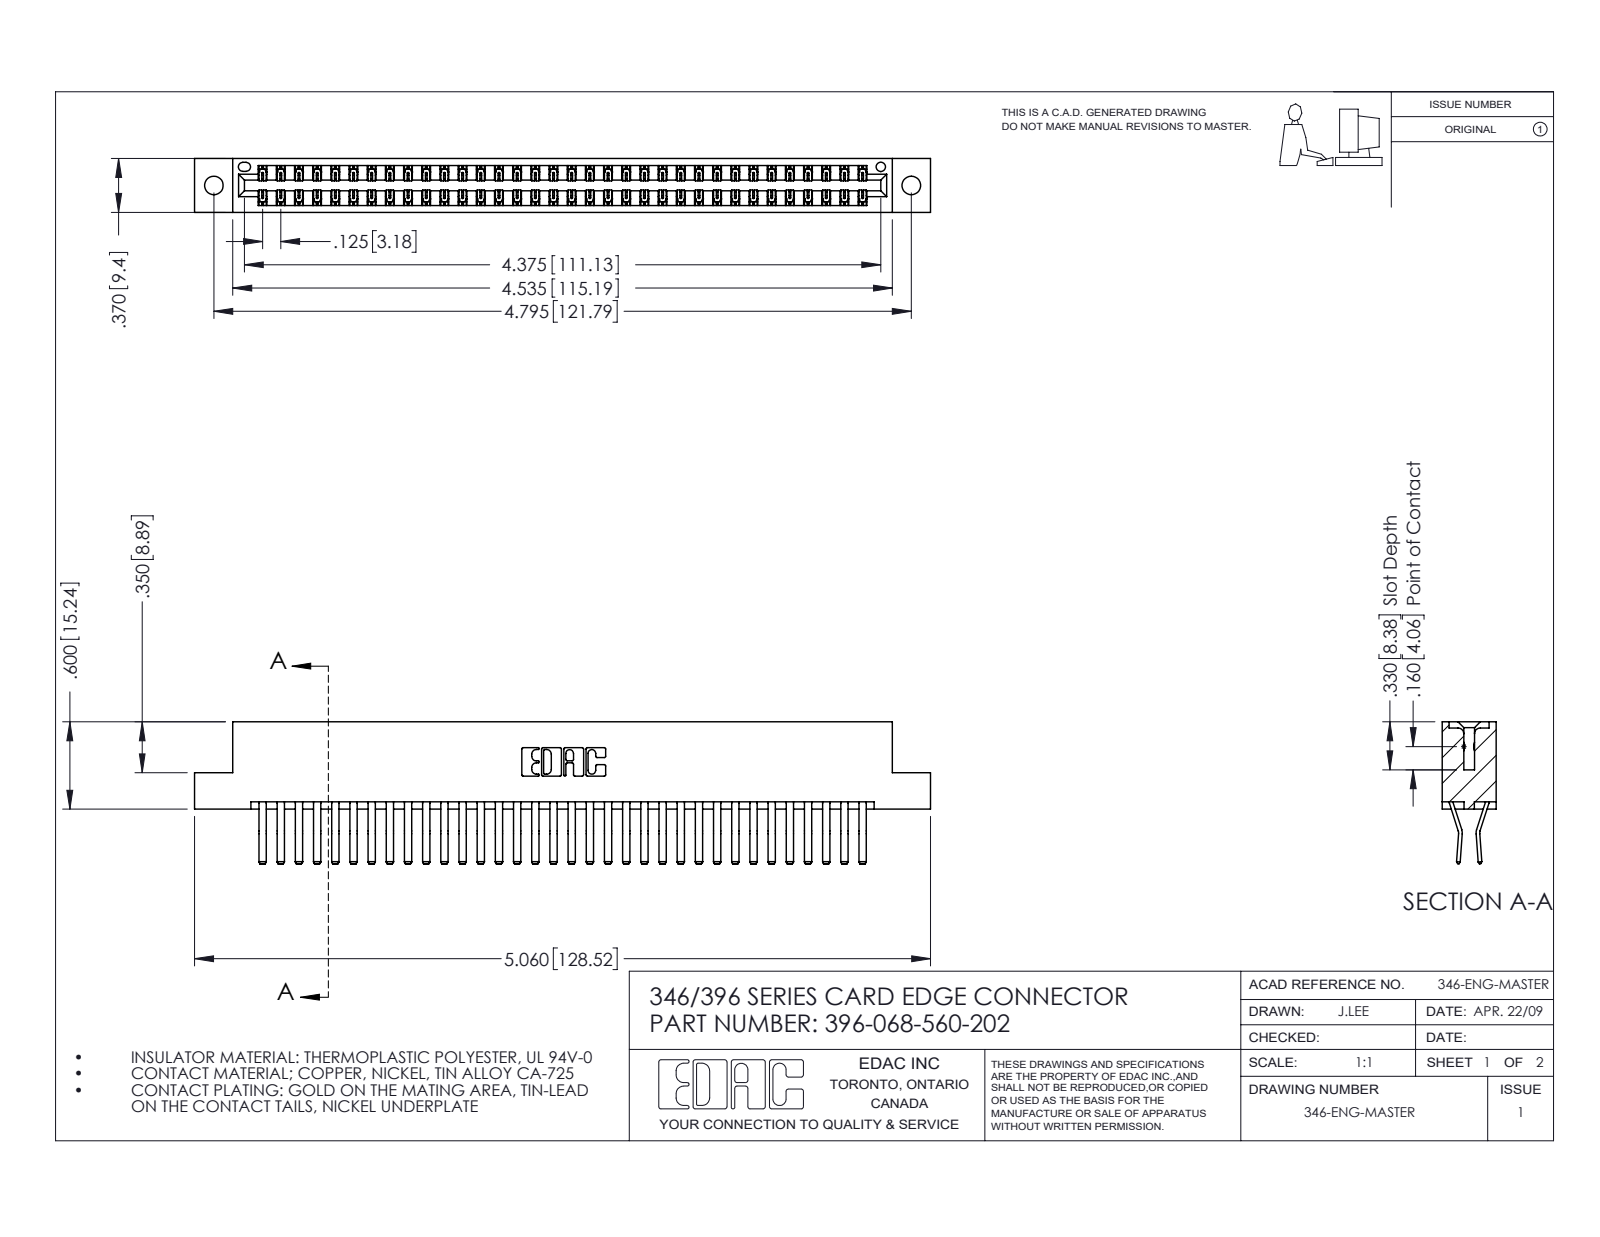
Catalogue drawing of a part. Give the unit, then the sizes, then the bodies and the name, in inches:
Units: inches
Overall size (bounding box): 5.06 × 0.975 × 0.37
Round holes (diameter × count): ⌀0.128 ×2, ⌀0.064 ×1
Partial cylindrical surfaces — rounded edges, fillets, slot ends (radius × count): R0.006 ×102, R0.01 ×22, R0.007 ×6, R0.031 ×6, R0.026 ×3, R0.01 ×2, R0.014 ×2, R0.022 ×2
Main face-to-face distances: 0.048, 0.322, 0.37, 0.25, 0.025, 0.072, 0.298, 0.275, 0.148, 0.222
Hole centre spacings: 0.246, 4.587, 4.795
Volume: 0.786 in³ · Surface area: 28.67 in²
Bodies: 69 solids, 3794 faces (2456 planar, 1338 cylindrical, 0 other)
Part name (STEP PRODUCT): 396-068-560-202; 345-292-001_560 Tail; 346 Part_Flush Mounting Lugs - 0.128 Dia
STEP written by: SolidWorks 2016 (CONFIG_CONTROL_DESIGN)
